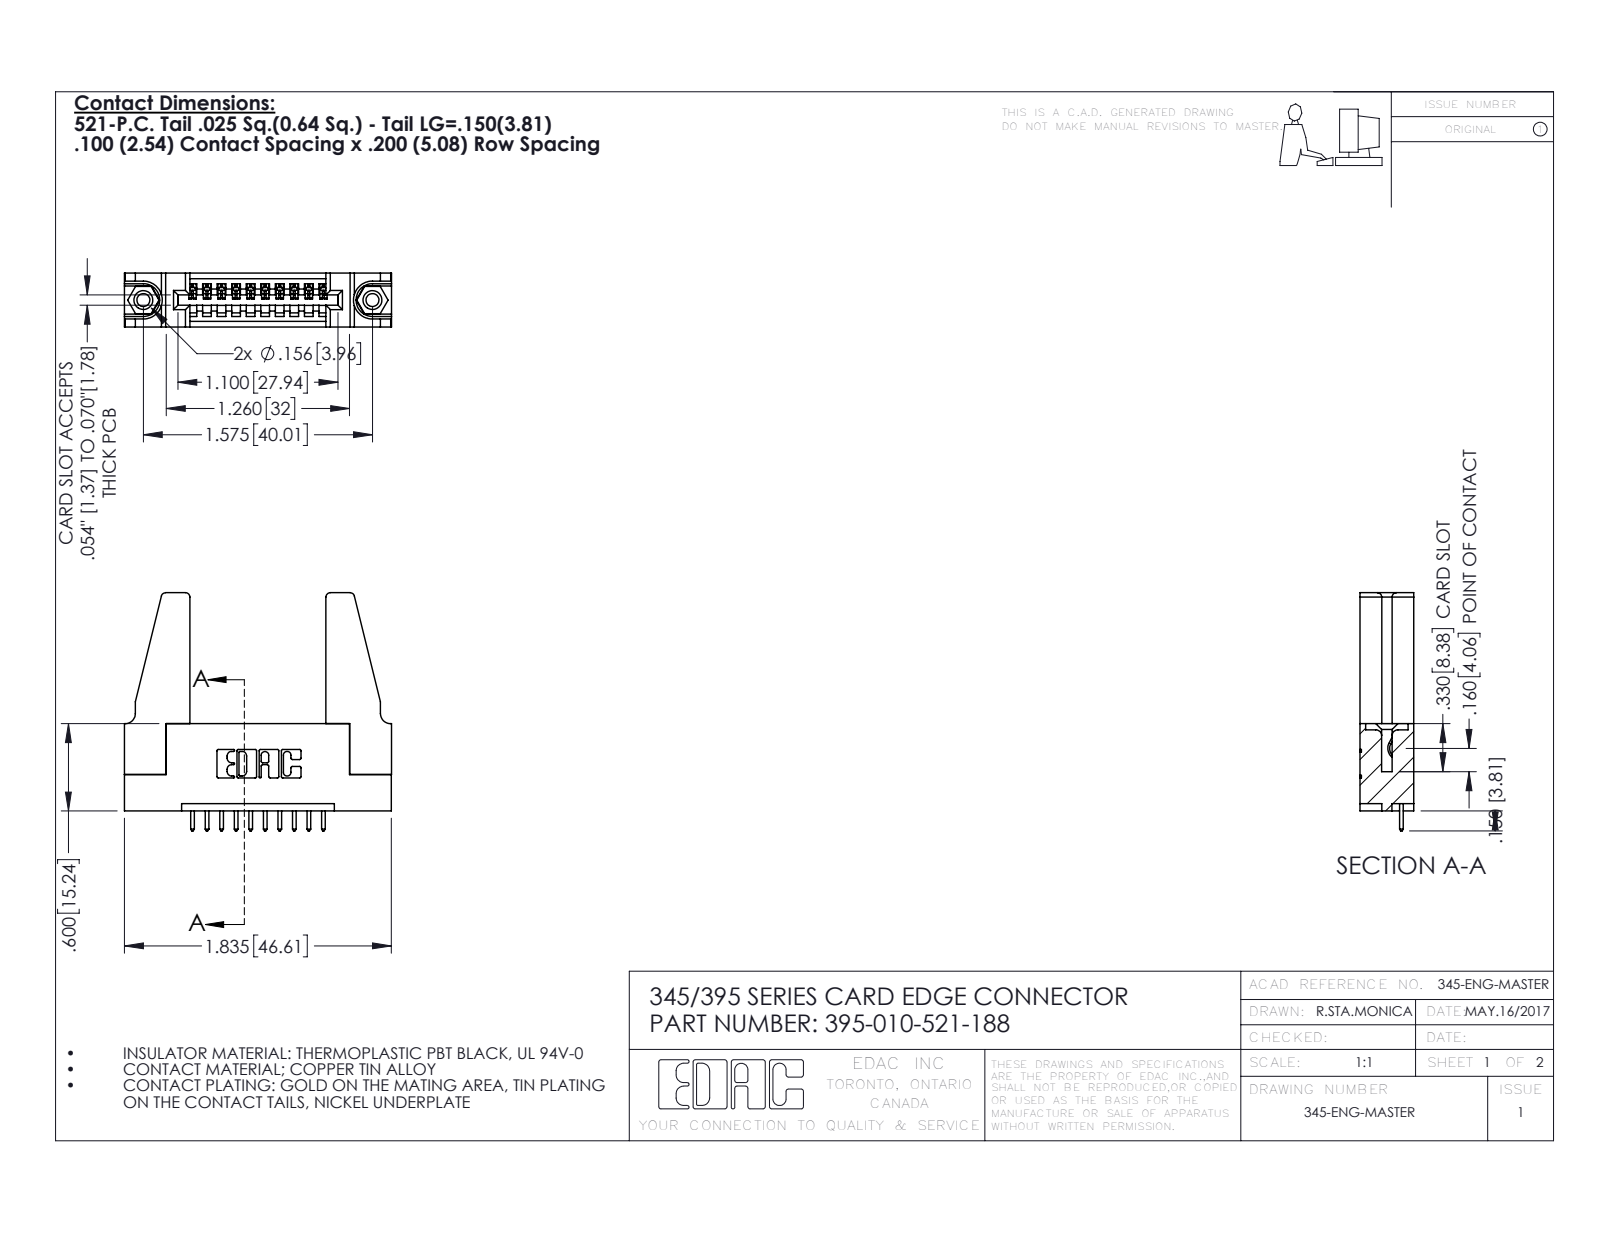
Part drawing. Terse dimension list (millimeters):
name: 395-010-521-188; 345-250-001_345-250-001-102; 345-292-001_345-293-121; 345 Part_Flush Mounting Lugs - 0.156 Dia-TH (+1 more)
written by: SolidWorks 2016 (CONFIG_CONTROL_DESIGN)
unit: mm
bodies: 15 solids, 830 faces (552 planar, 262 cylindrical, 16 other)
size: 46.6 × 41.6 × 9.4
volume: 7 390 mm³; area: 8 084 mm²
holes: 2× ⌀2.3, 2× ⌀3.2, 2× ⌀4, 1× ⌀1.6
bosses: 2× ⌀3.9
rounds: 22× R0.3, 20× R0.2, 20× R0.3, 8× R0.8, 6× R0.2, 6× R0.8, 3× R0.7, 2× R0.8
face distances: 9.4, 1.8, 7.6, 5.1, 2.5, 6.9, 0.6, 3.8, 3.8, 6.4
hole spacings: 6.9, 34.1, 40
